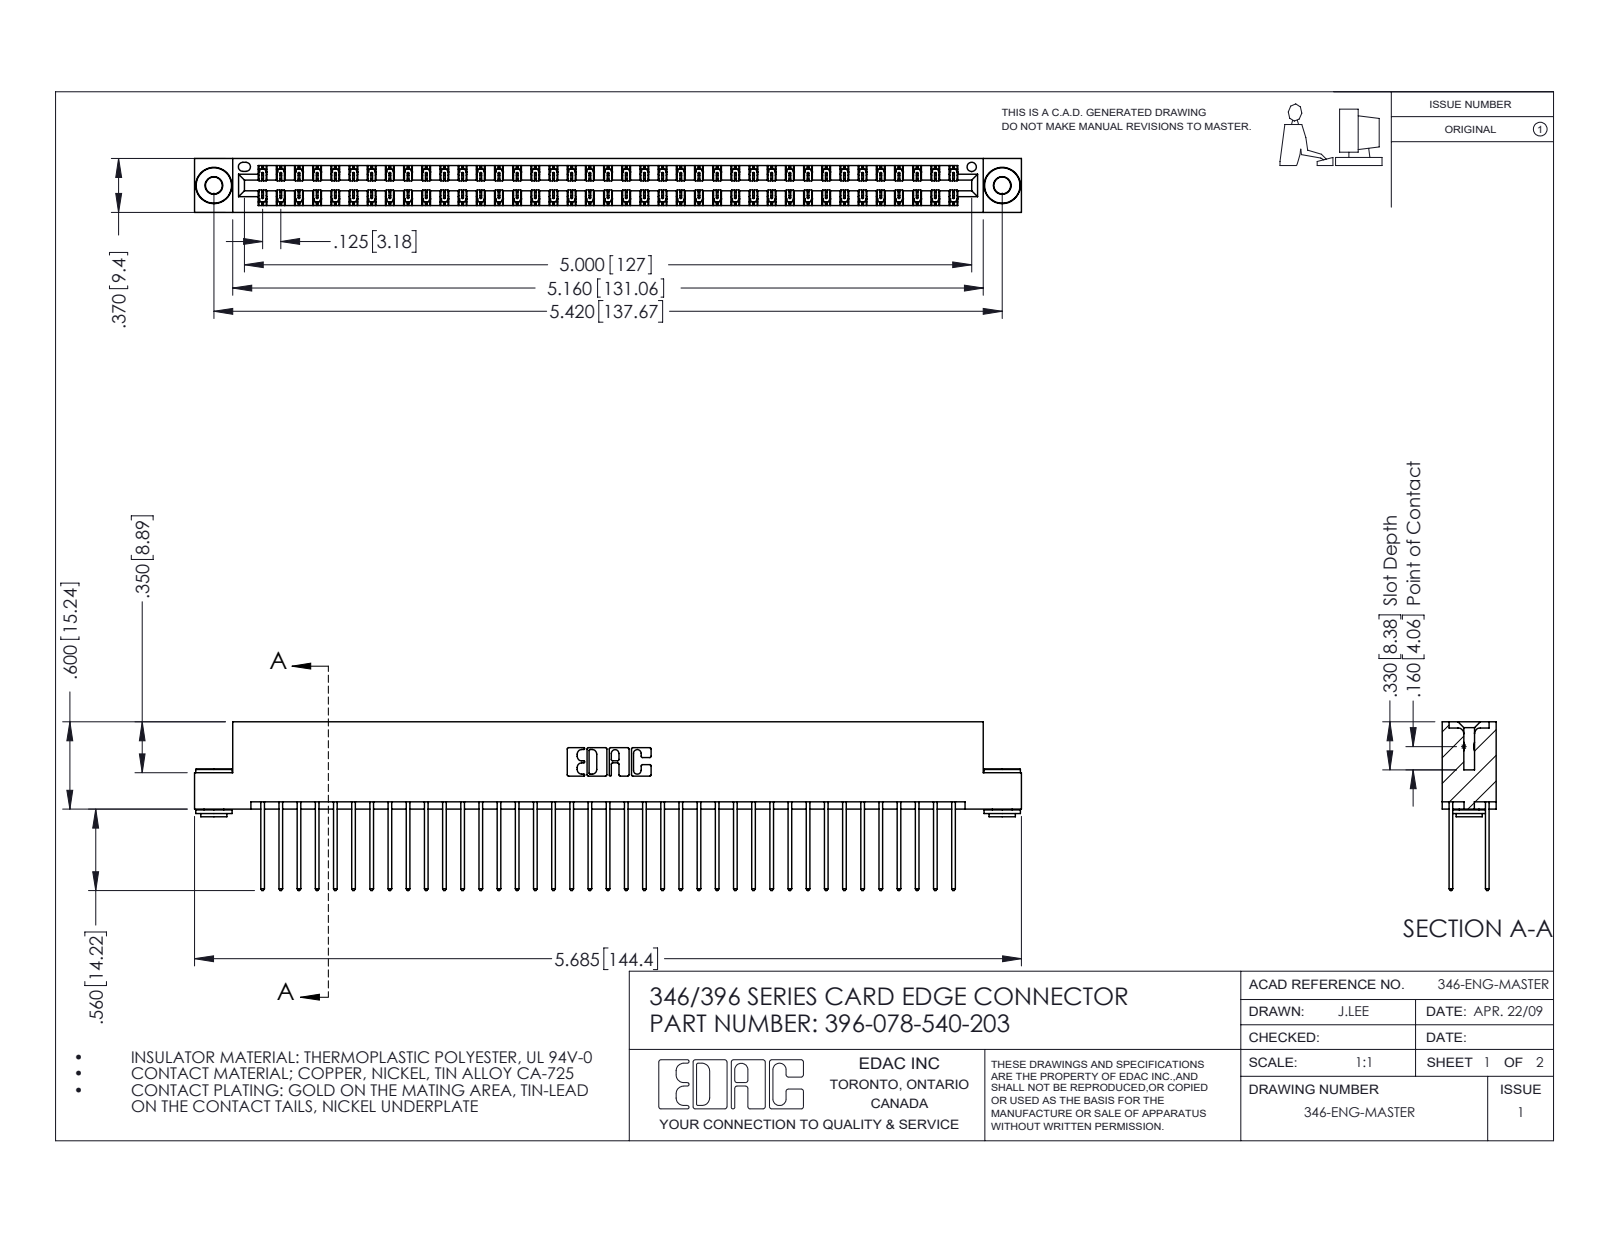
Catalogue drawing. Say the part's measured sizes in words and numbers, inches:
The part is named "345-250-002_345-250-002-102; 396-078-540-203; 345-292-001_345-293-140; 346 Part_Flush Mounting Lugs - 0.156 Dia-TH". Its 3-D file was written by "SolidWorks 2016 (CONFIG_CONTROL_DESIGN)". It is 81 solids with 4216 faces: 2816 planar, 1392 cylindrical and 8 other. Overall it measures 5.685 by 1.16 by 0.37 inches. Its volume is 0.877 cubic inches and its surface area 33.05 square inches. Round holes: 2 of diameter 0.116, 2 of diameter 0.156, 1 of diameter 0.064. Round bosses or shafts: 2 of diameter 0.25, 2 of diameter 0.18, 2 of diameter 0.136. Partial cylindrical surfaces (rounded edges, fillets, slot ends): 117 of radius 0.006, 78 of radius 0.01, 22 of radius 0.01, 6 of radius 0.007, 6 of radius 0.031, 3 of radius 0.026, 2 of radius 0.014, 2 of radius 0.022. The main face-to-face distances are 0.048, 0.322, 0.25, 0.025, 0.072, 0.298, 0.37, 0.275, 0.148, 0.222. The hole center spacings are 0.246, 5.211, 5.42.
